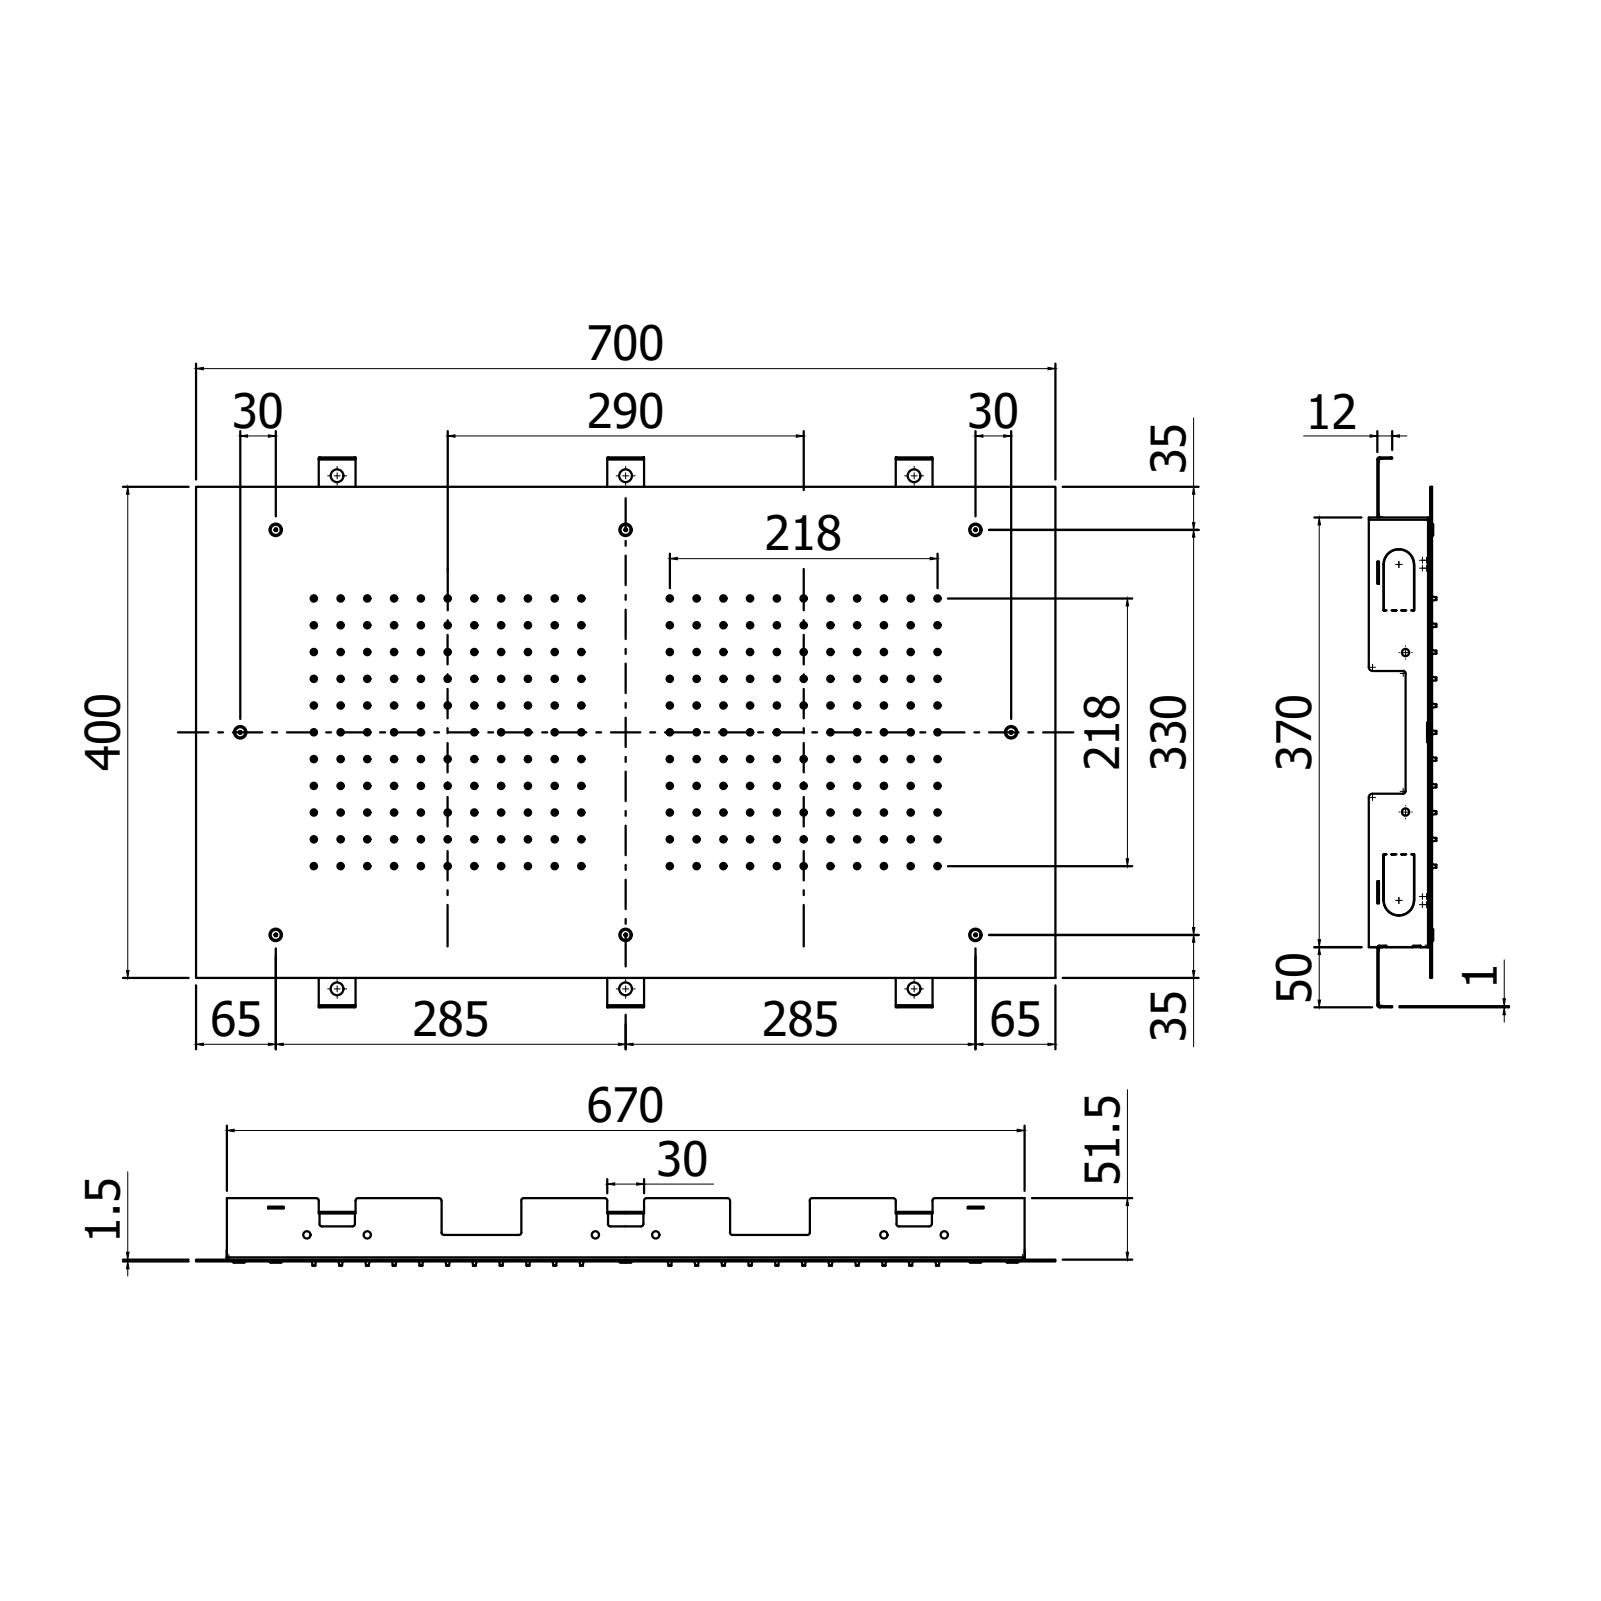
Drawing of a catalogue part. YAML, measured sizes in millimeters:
part_name: "ZSOF302CR"
step_written_by: "CREO PARAMETRIC BY PTC INC, 2020044 (CONFIG_CONTROL_DESIGN)"
units: millimeters
bodies: {solids: 1, faces: 4310, planar: 330, cylindrical: 1548, other: 2432}
overall_size: [700, 400, 5.8]
volume: 421275
surface_area: 833343
round_holes:
  - {diameter: 1.5, count: 240}
  - {diameter: 3.1, count: 240}
  - {diameter: 5, count: 240}
  - {diameter: 7, count: 8}
round_bosses_or_shafts:
  - {diameter: 10, count: 8}
  - {diameter: 5, count: 8}
partial_cylinders:
  - {radius: 0.2, count: 48}
  - {radius: 0.1, count: 8}
  - {radius: 2, count: 4}
face_to_face_distances: [1.5, 1, 2.5, 75, 325, 400, 250, 700, 375, 625]
hole_center_spacings: [48.75, 68.94, 30.83, 78.6, 109, 43.6, 89.88, 111.16]
